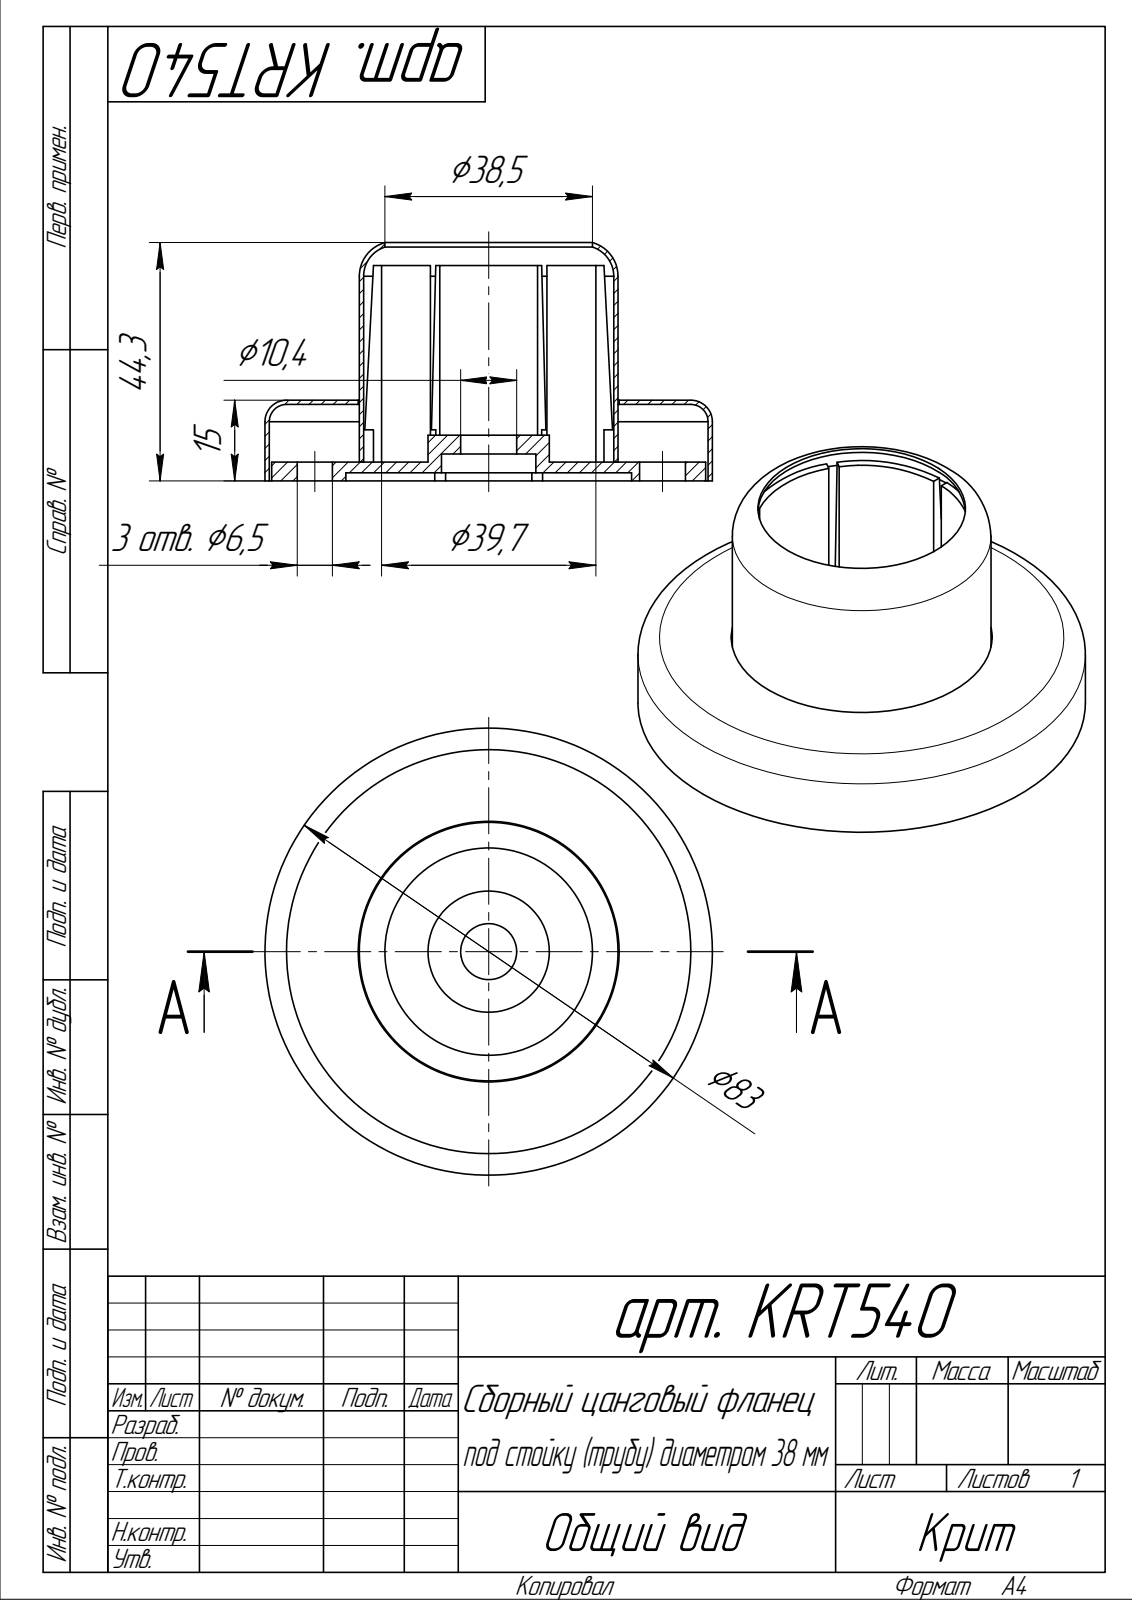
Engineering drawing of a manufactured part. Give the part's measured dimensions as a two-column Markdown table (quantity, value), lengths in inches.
| quantity | value |
| --- | --- |
| part name | арт. KRT540; арт. KRT540.002; арт. KRT540.001; арт. KRT540.003 |
| STEP written by | SolidWorks 2014 (AUTOMOTIVE_DESIGN) |
| units | inches |
| bodies | 3 solids, 107 faces (39 planar, 53 cylindrical, 15 other) |
| overall size | 3.268 × 3.268 × 1.743 |
| volume | 2.128 in³ |
| surface area | 74.9 in² |
| round holes (diameter × count) | 0.256 × 3, 0.335 × 3, 0.409 × 1, 0.689 × 1, 1.516 × 1, 1.567 × 1, 1.827 × 1, 1.906 × 1, 3.205 × 1 |
| round bosses / shafts (diameter × count) | 3.268 × 1, 3.169 × 1, 1.89 × 1, 1.685 × 1, 0.886 × 1 |
| partial cylindrical surfaces (radius × count) | 0.079 × 4, 1.043 × 1 |
| main face-to-face distances | 0.138, 0.559, 0.591, 0.421, 0.453, 0.031, 0.079, 0.059, 0.5, 0.531 |
| hole center spacings | 1.27, 2.199, 2.539, 2.199, 1.269, 1.27 |
